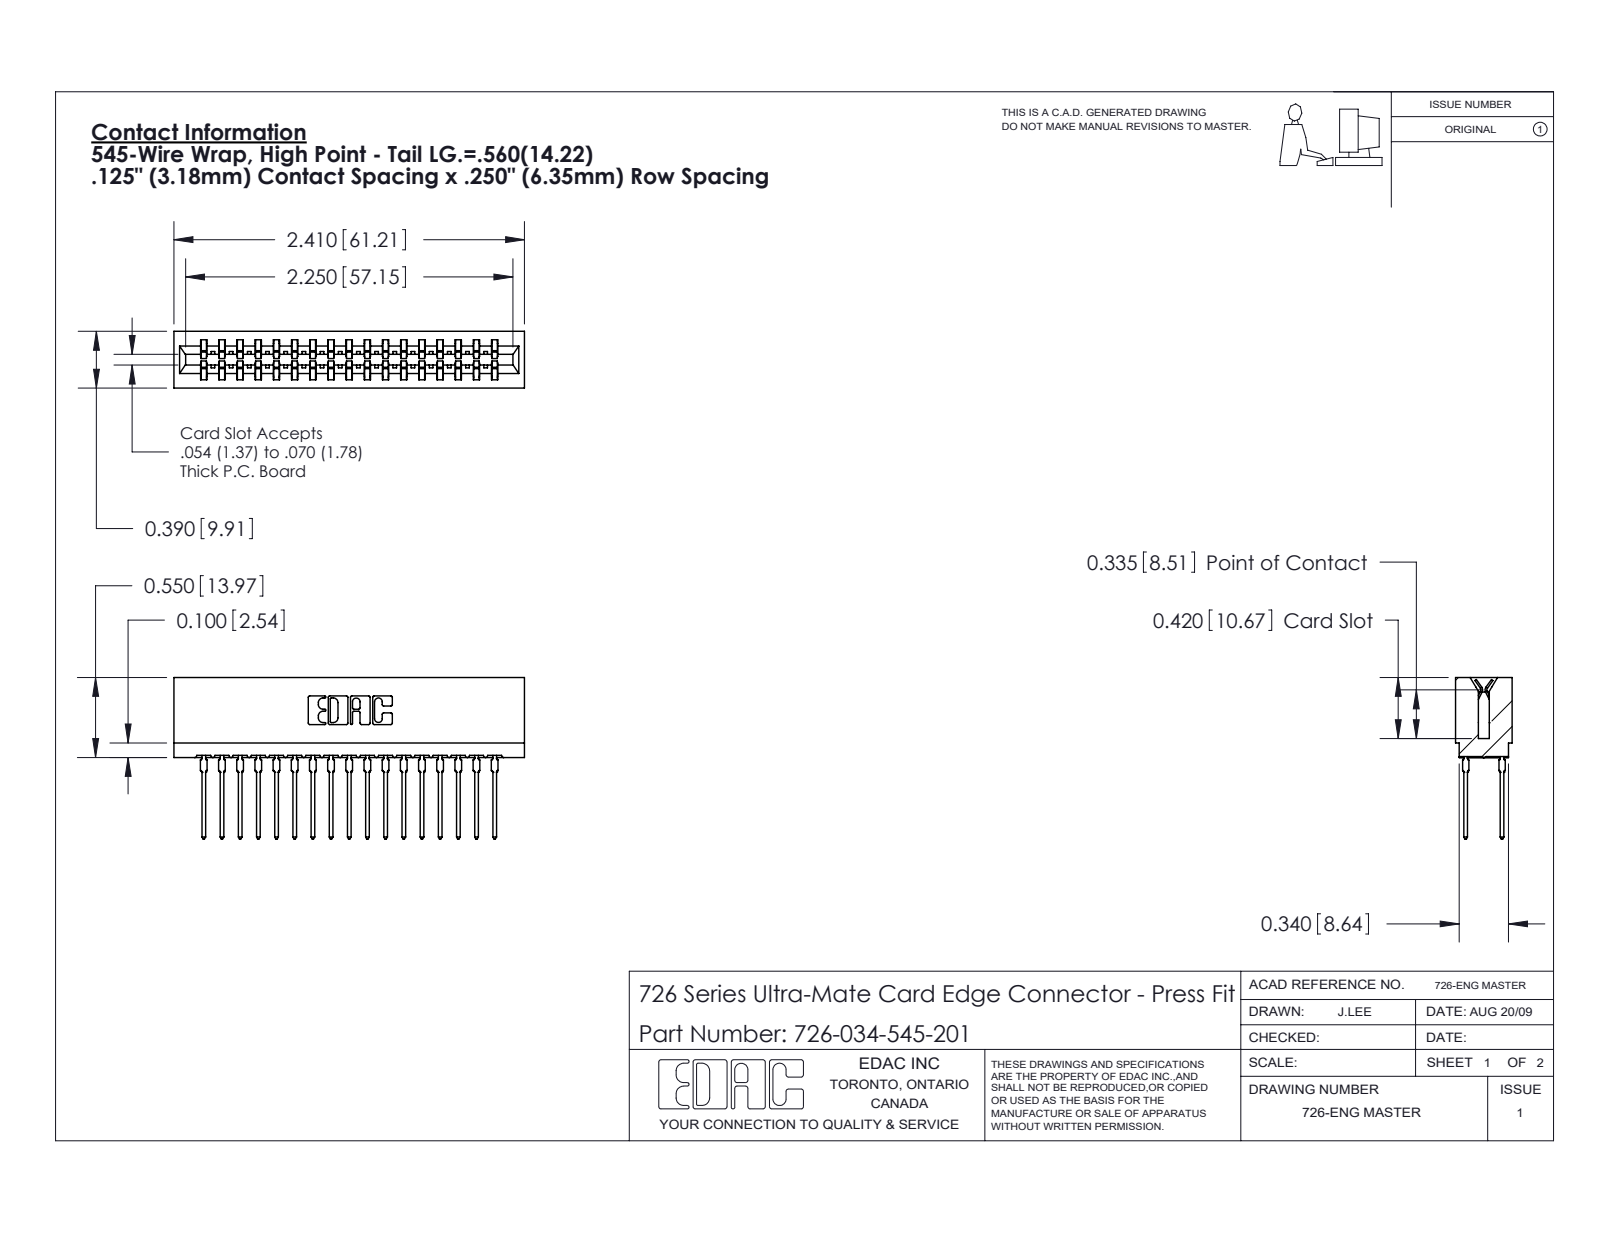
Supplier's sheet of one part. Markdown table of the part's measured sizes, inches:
| quantity | value |
| --- | --- |
| part name | 726 Part_.515 Slot Depth - 01; 726-034-545-201; 746-292-001_545 |
| STEP written by | SolidWorks 2020 (CONFIG_CONTROL_DESIGN) |
| units | inches |
| bodies | 35 solids, 3140 faces (1619 planar, 637 cylindrical, 884 other) |
| overall size | 2.41 × 1.109 × 0.39 |
| volume | 0.359 in³ |
| surface area | 15.35 in² |
| partial cylindrical surfaces (radius × count) | 0.021 × 68, 0.01 × 22, 0.015 × 18, 0.005 × 8, 0.011 × 8, 0.007 × 6, 0.031 × 6, 0.026 × 3 |
| main face-to-face distances | 0.057, 0.333, 0.25, 0.025, 0.307, 0.083, 0.39, 0.5, 0.275, 0.75 |
